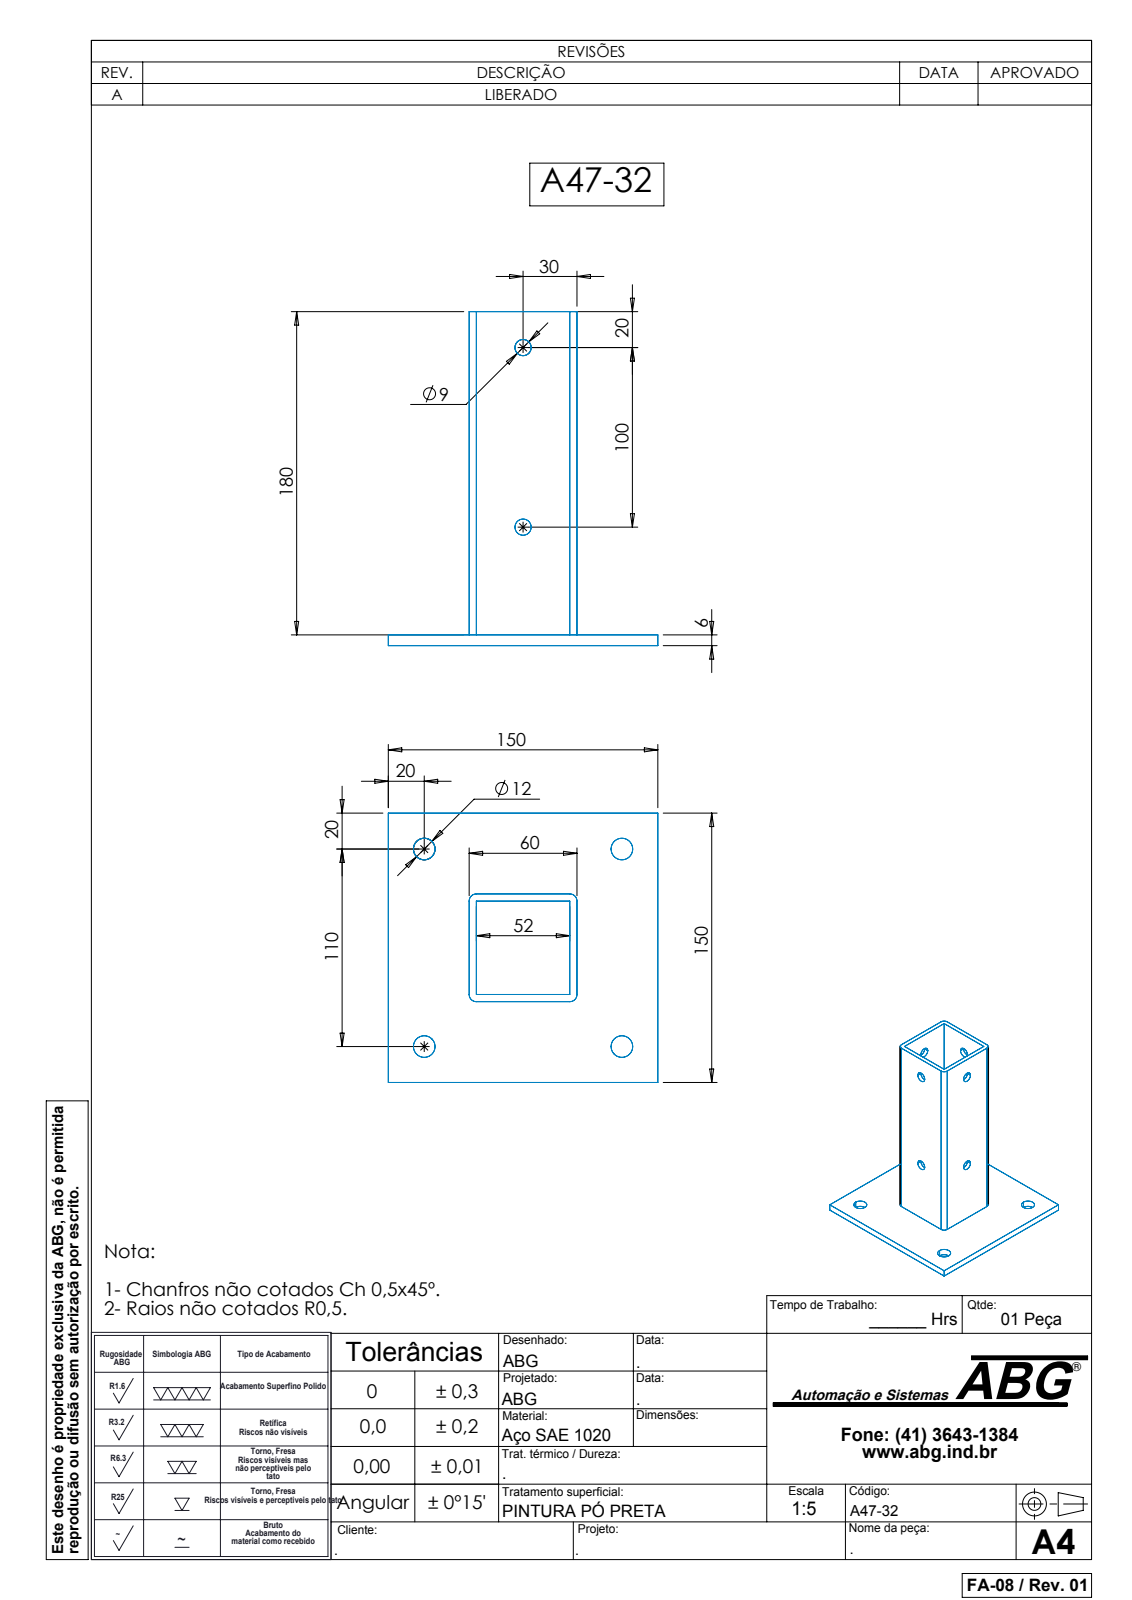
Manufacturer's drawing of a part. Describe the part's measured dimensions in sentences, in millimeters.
The part is named "A47-32". Its 3-D file was written by "SolidWorks 2007 (CONFIG_CONTROL_DESIGN)". It is 1 solid with 44 faces: 16 planar, 28 cylindrical and 0 other. Overall it measures 186 by 150 by 150 millimeters. Its volume is 289 058 cubic millimeters and its surface area 127 891 square millimeters. Round holes: 4 of diameter 9, 4 of diameter 12. Partial cylindrical surfaces (rounded edges, fillets, slot ends): 4 of radius 4. The main face-to-face distances are 4, 56, 6, 60, 52, 45, 49, 101, 105, 150. The hole center spacings are 110, 100, 155.56.
